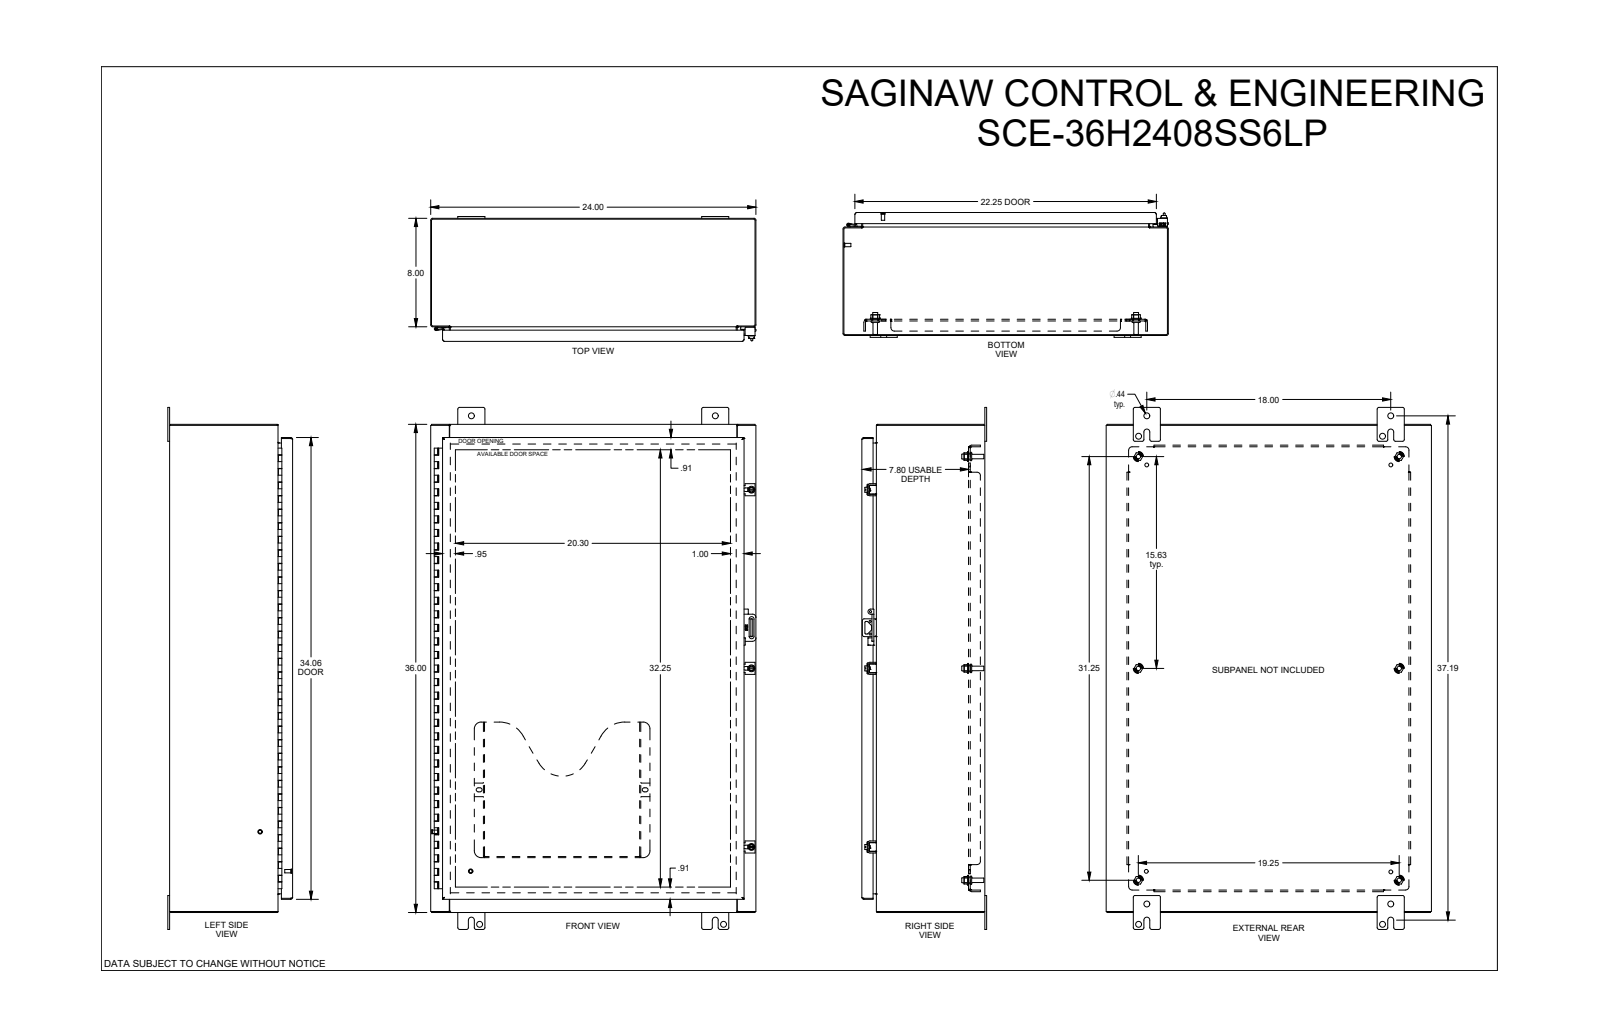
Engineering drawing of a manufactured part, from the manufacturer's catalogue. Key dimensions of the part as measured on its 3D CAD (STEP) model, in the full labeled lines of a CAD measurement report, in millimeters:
Part name (STEP PRODUCT): SCE-36H2408SS6LP
STEP written by: SolidWorks 2019 (CONFIG_CONTROL_DESIGN)
Units: millimetres
Bodies: 0 solids, 4019 faces (1647 planar, 844 cylindrical, 1528 other)
Overall size (bounding box): 977.9 × 609.6 × 233.9
Round holes (diameter × count): ⌀11.1 ×8, ⌀6.4 ×6, ⌀9.3 ×6, ⌀12.7 ×6, ⌀4.8 ×5, ⌀4.9 ×5, ⌀7.1 ×4, ⌀5.2 ×3, ⌀4.1 ×2, ⌀3.3 ×1, ⌀3.4 ×1
Round bosses / shafts (diameter × count): ⌀6.3 ×8, ⌀14.3 ×6, ⌀9.3 ×6, ⌀8.4 ×6, ⌀6.5 ×5, ⌀4.8 ×5, ⌀6.4 ×4, ⌀12.9 ×3
Partial cylindrical surfaces — rounded edges, fillets, slot ends (radius × count): R0.3 ×160, R0.4 ×44, R0.7 ×36, R1.5 ×29, R0.8 ×27, R3.2 ×27, R1 ×22, R1.8 ×14
Main face-to-face distances: 1.9, 1.9, 228.5, 226.6, 30.5, 200, 230.5, 228.5, 201.2, 28.6
Hole centre spacings: 41.1, 457.2, 914.4, 1022.3, 13.1, 200, 200, 381.5
